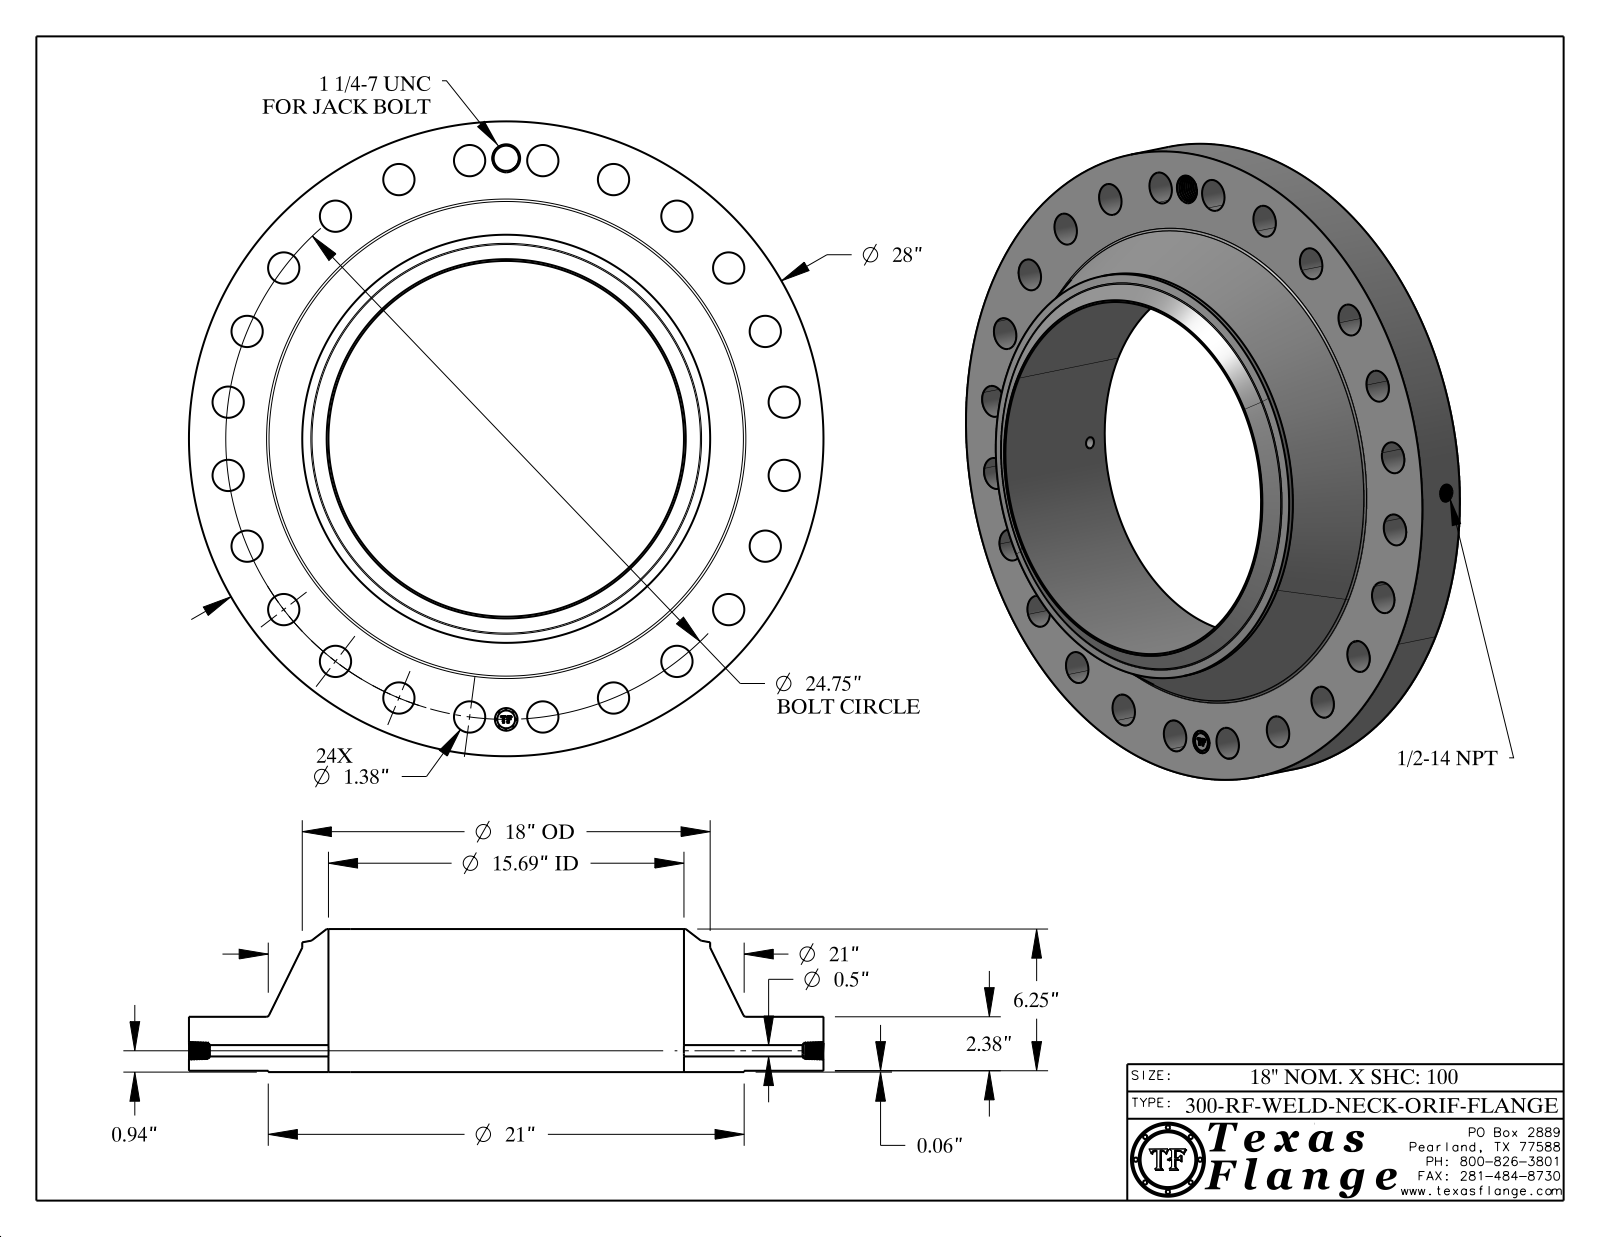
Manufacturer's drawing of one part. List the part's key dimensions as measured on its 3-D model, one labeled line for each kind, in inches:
Part name (STEP PRODUCT): 300-RF-WELD-NECK
STEP written by: CATIA V5 STEP AP214 (AUTOMOTIVE_DESIGN)
Units: inches
Bodies: 1 solid, 817 faces (369 planar, 129 cylindrical, 319 other)
Overall size (bounding box): 28 × 28 × 6.31
Volume: 1 276 in³ · Surface area: 1 716 in²
Round holes (diameter × count): ⌀1.38 ×24, ⌀0.5 ×1, ⌀0.672 ×1, ⌀1 ×1, ⌀1.109 ×1, ⌀15.688 ×1
Round bosses / shafts (diameter × count): ⌀0.061 ×8, ⌀28 ×1, ⌀21 ×1, ⌀18 ×1, ⌀0.788 ×1
Main face-to-face distances: 2.38, 0.06, 2.44, 6.31, 6.25, 3.87, 0.015, 2.425, 2.365, 3.885
Hole centre spacings: 12.375, 15.067, 21.434, 22.866, 23.907, 6.406, 17.501, 3.23
